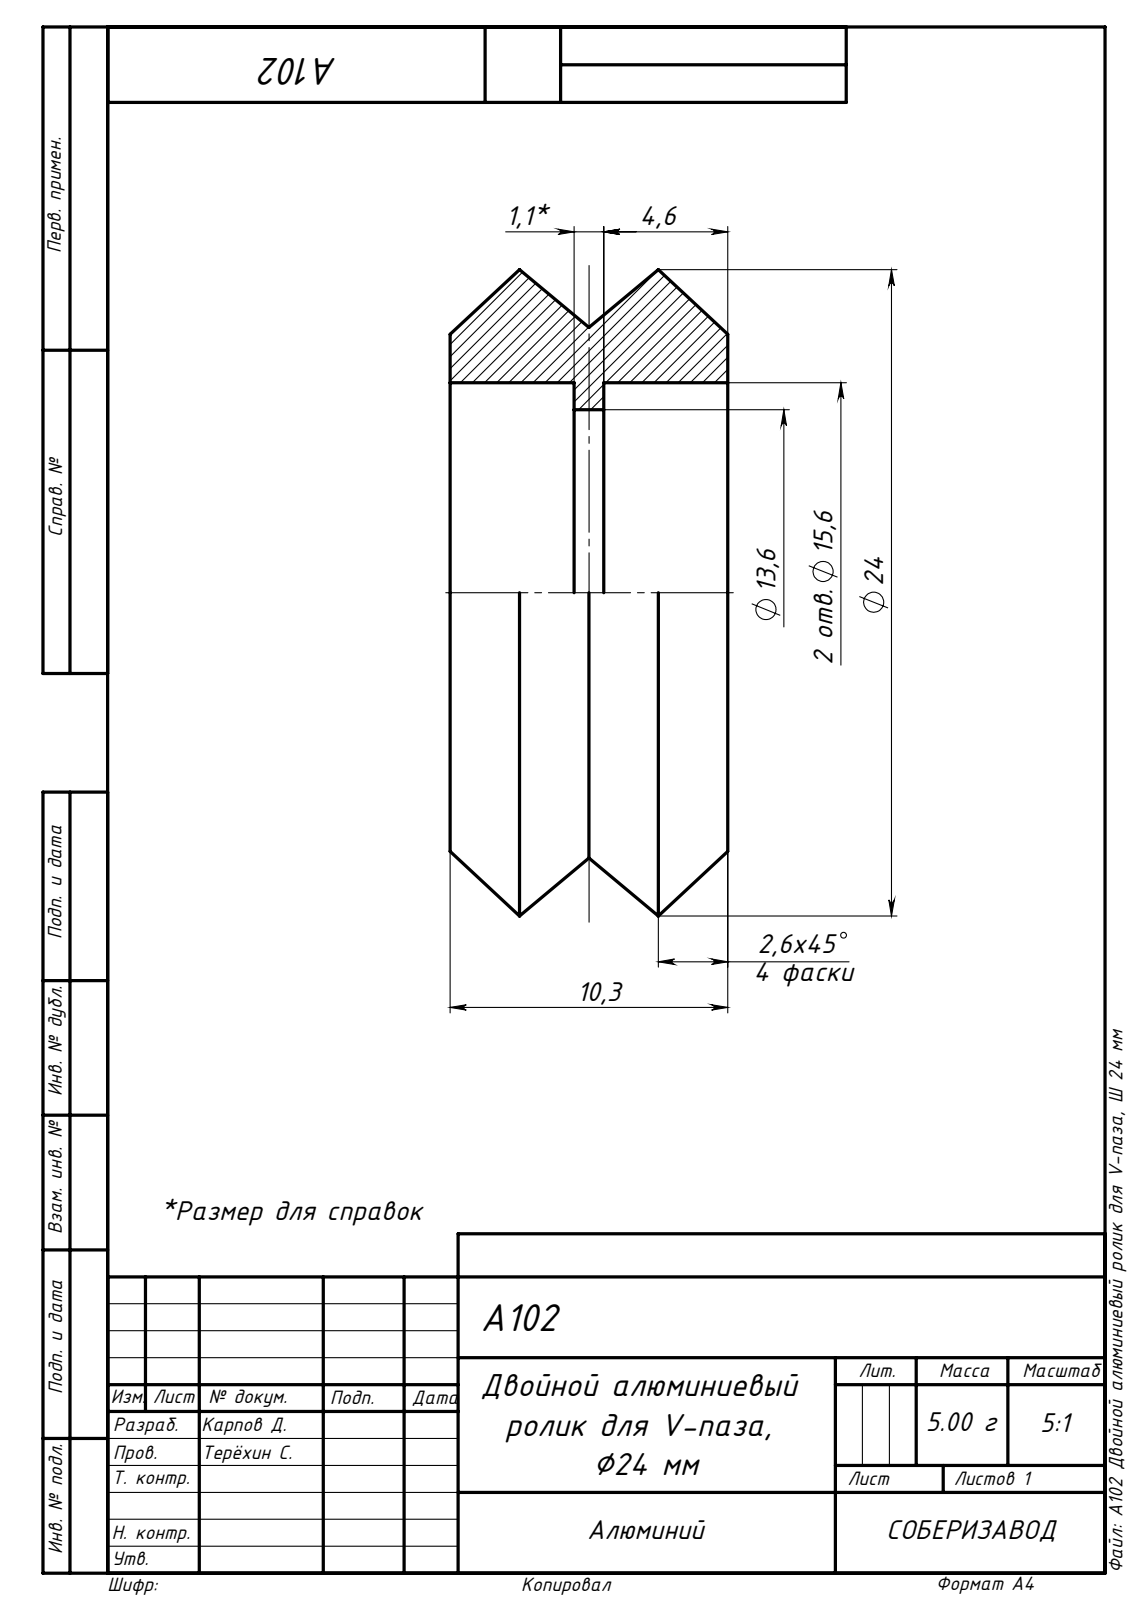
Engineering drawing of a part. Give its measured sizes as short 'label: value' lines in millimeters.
written by: SolidWorks 2018 (AUTOMOTIVE_DESIGN)
unit: mm
bodies: 1 solid, 18 faces (4 planar, 6 cylindrical, 8 other)
size: 24 × 24 × 10.3
volume: 1 914 mm³; area: 1 725 mm²
holes: 1× ⌀13.6, 1× ⌀15.6
face distances: 10.3, 4.6, 5.7, 1.1
